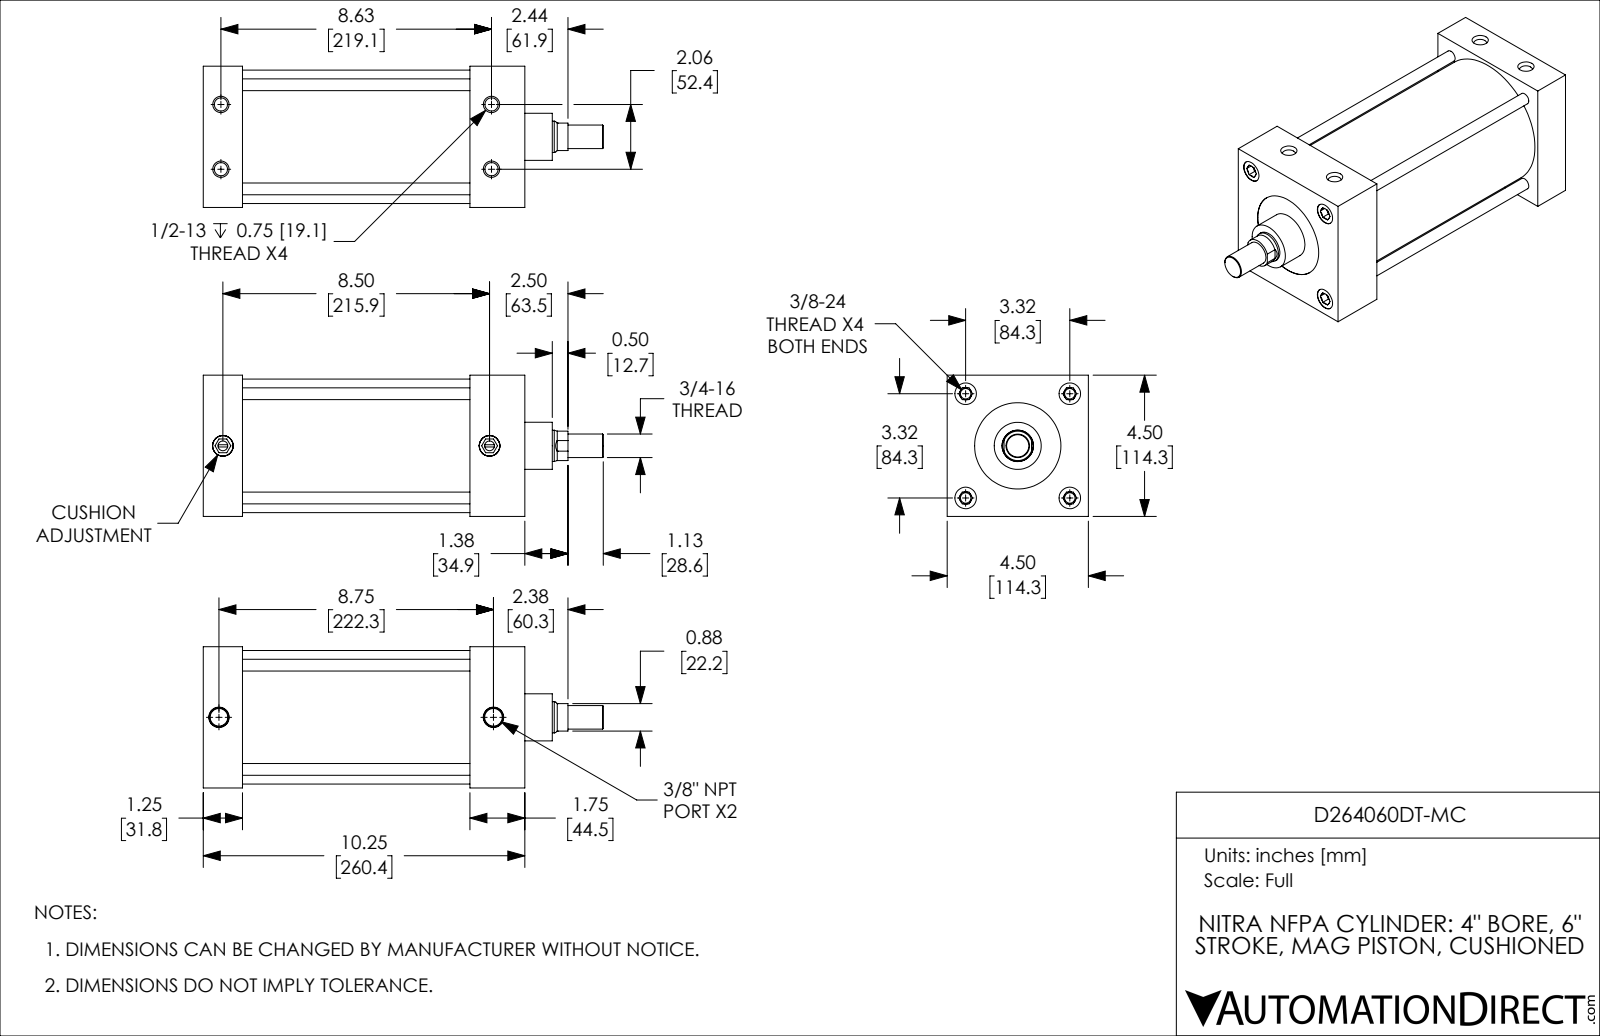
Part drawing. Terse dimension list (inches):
name: D264060DT-MC_PISTON_KK1; D264060DT-MC; D264060DT-MC_CUSHION; D264060DT-MC_BODY
written by: SolidWorks 2019 (CONFIG_CONTROL_DESIGN)
unit: in
bodies: 4 solids, 246 faces (90 planar, 78 cylindrical, 78 other)
size: 12.75 × 4.5 × 4.5
volume: 96.06 in³; area: 459.4 in²
holes: 4× ⌀0.332, 4× ⌀0.422, 4× ⌀0.687, 2× ⌀0.312, 2× ⌀0.562, 2× ⌀0.656, 1× ⌀1.001, 1× ⌀2.75, 1× ⌀4.001
bosses: 4× ⌀0.375, 2× ⌀0.657, 1× ⌀4.251, 1× ⌀3.999, 1× ⌀1.5, 1× ⌀0.999, 1× ⌀0.75
rounds: 1× R0.469
face distances: 1.25, 4.5, 8.5, 7.25, 10.25, 9, 1.75, 2.5, 6, 7.75
hole spacings: 1.033, 2.347, 3.32, 8.748, 2.062, 4.695, 8.625, 8.868
